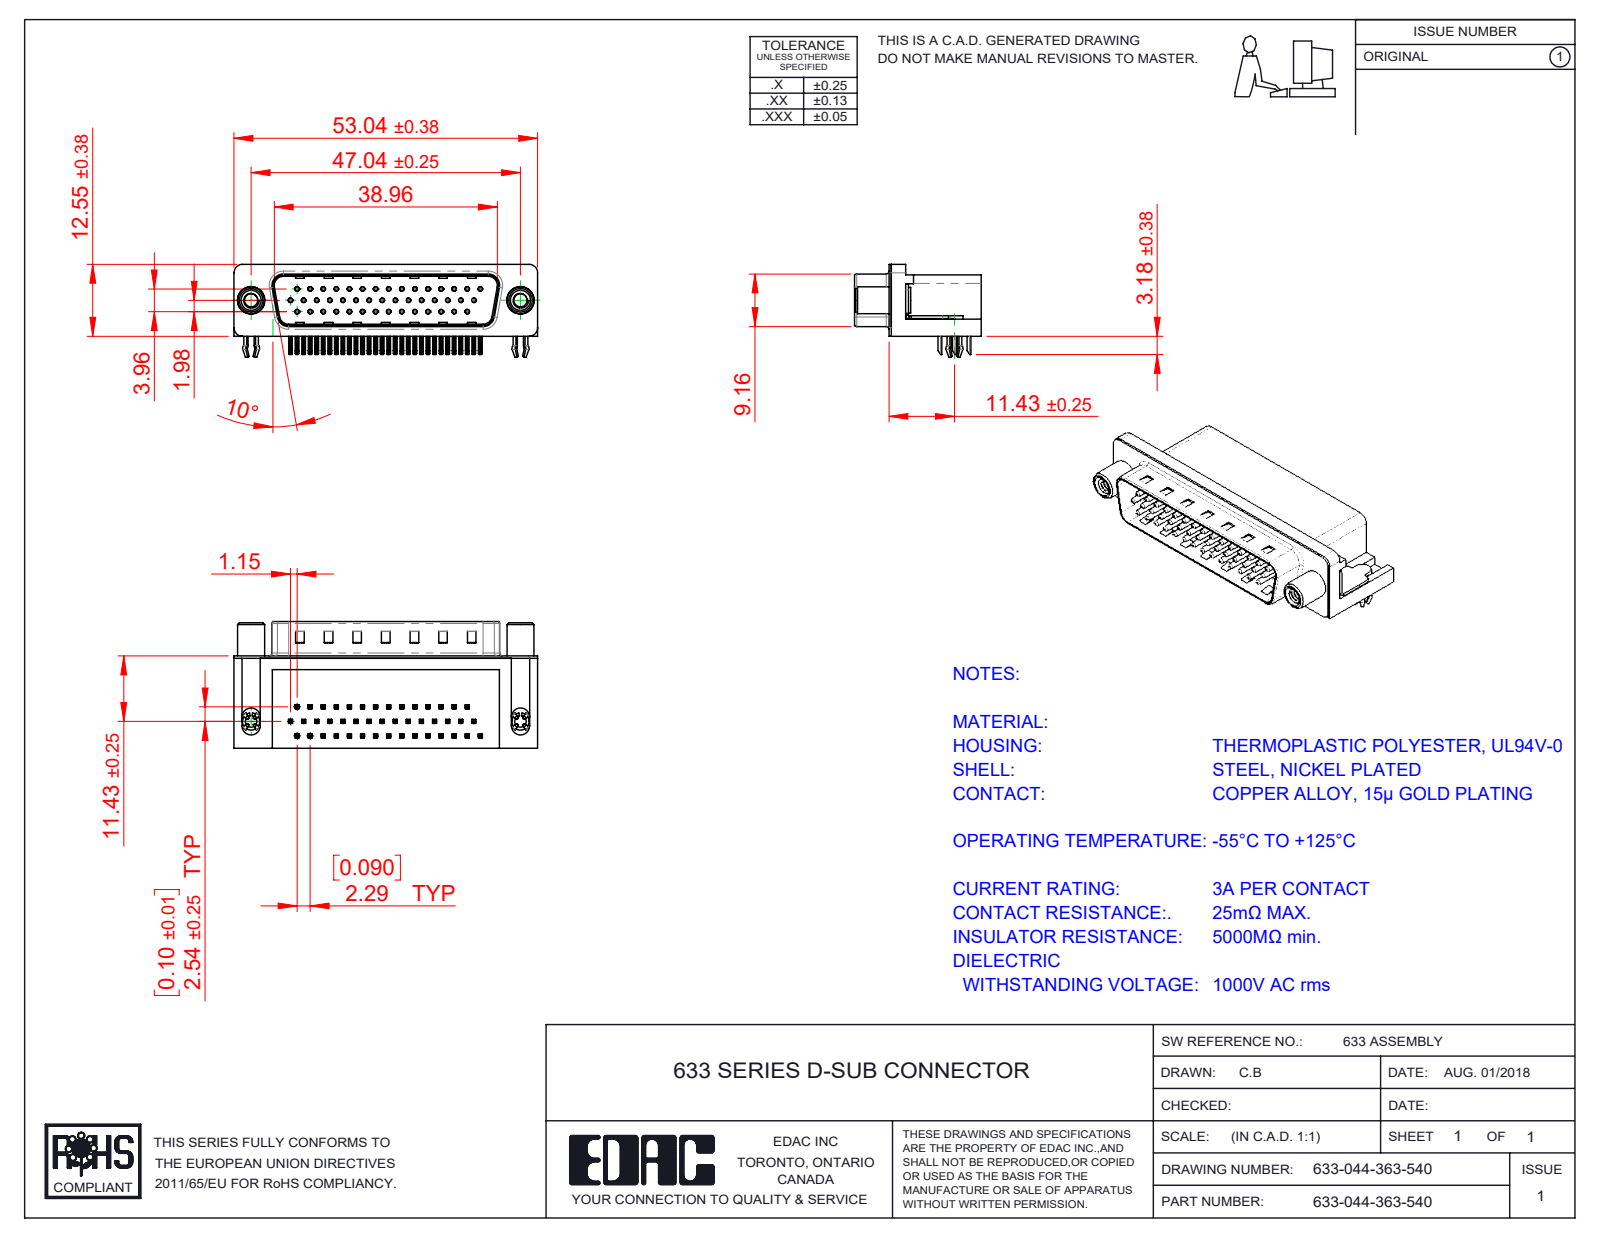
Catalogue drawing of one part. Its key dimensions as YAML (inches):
part_name: "633 Contact Bottom; 633 Round Threaded Standoff; 633 Contact Top; 633 4 Prong Board Lock (+4 more)"
step_written_by: "SolidWorks 2016 (CONFIG_CONTROL_DESIGN)"
units: inches
bodies: {solids: 50, faces: 3804, planar: 2351, cylindrical: 1074, other: 379}
overall_size: [2.088, 0.87, 0.64]
volume: 0.501
surface_area: 16.26
round_holes:
  - {diameter: 0.014, count: 44}
  - {diameter: 0.031, count: 44}
  - {diameter: 0.079, count: 2}
  - {diameter: 0.091, count: 2}
  - {diameter: 0.122, count: 2}
  - {diameter: 0.157, count: 2}
  - {diameter: 0.189, count: 2}
  - {diameter: 0.197, count: 2}
round_bosses_or_shafts:
  - {diameter: 0.03, count: 44}
  - {diameter: 0.193, count: 2}
  - {diameter: 0.185, count: 2}
  - {diameter: 0.177, count: 2}
  - {diameter: 0.152, count: 2}
  - {diameter: 0.118, count: 2}
partial_cylinders:
  - {radius: 0.01, count: 180}
  - {radius: 0.005, count: 88}
  - {radius: 0.039, count: 16}
  - {radius: 0.02, count: 9}
  - {radius: 0.063, count: 8}
  - {radius: 0.059, count: 7}
  - {radius: 0.035, count: 4}
  - {radius: 0.079, count: 4}
face_to_face_distances: [0.016, 0.407, 0.618, 0.114, 0.345, 0.098, 0.083, 0.1, 0.634, 0.421]
hole_center_spacings: [0.09, 0.18, 0.18, 0.09, 0.27, 0.361, 0.451, 0.089]
